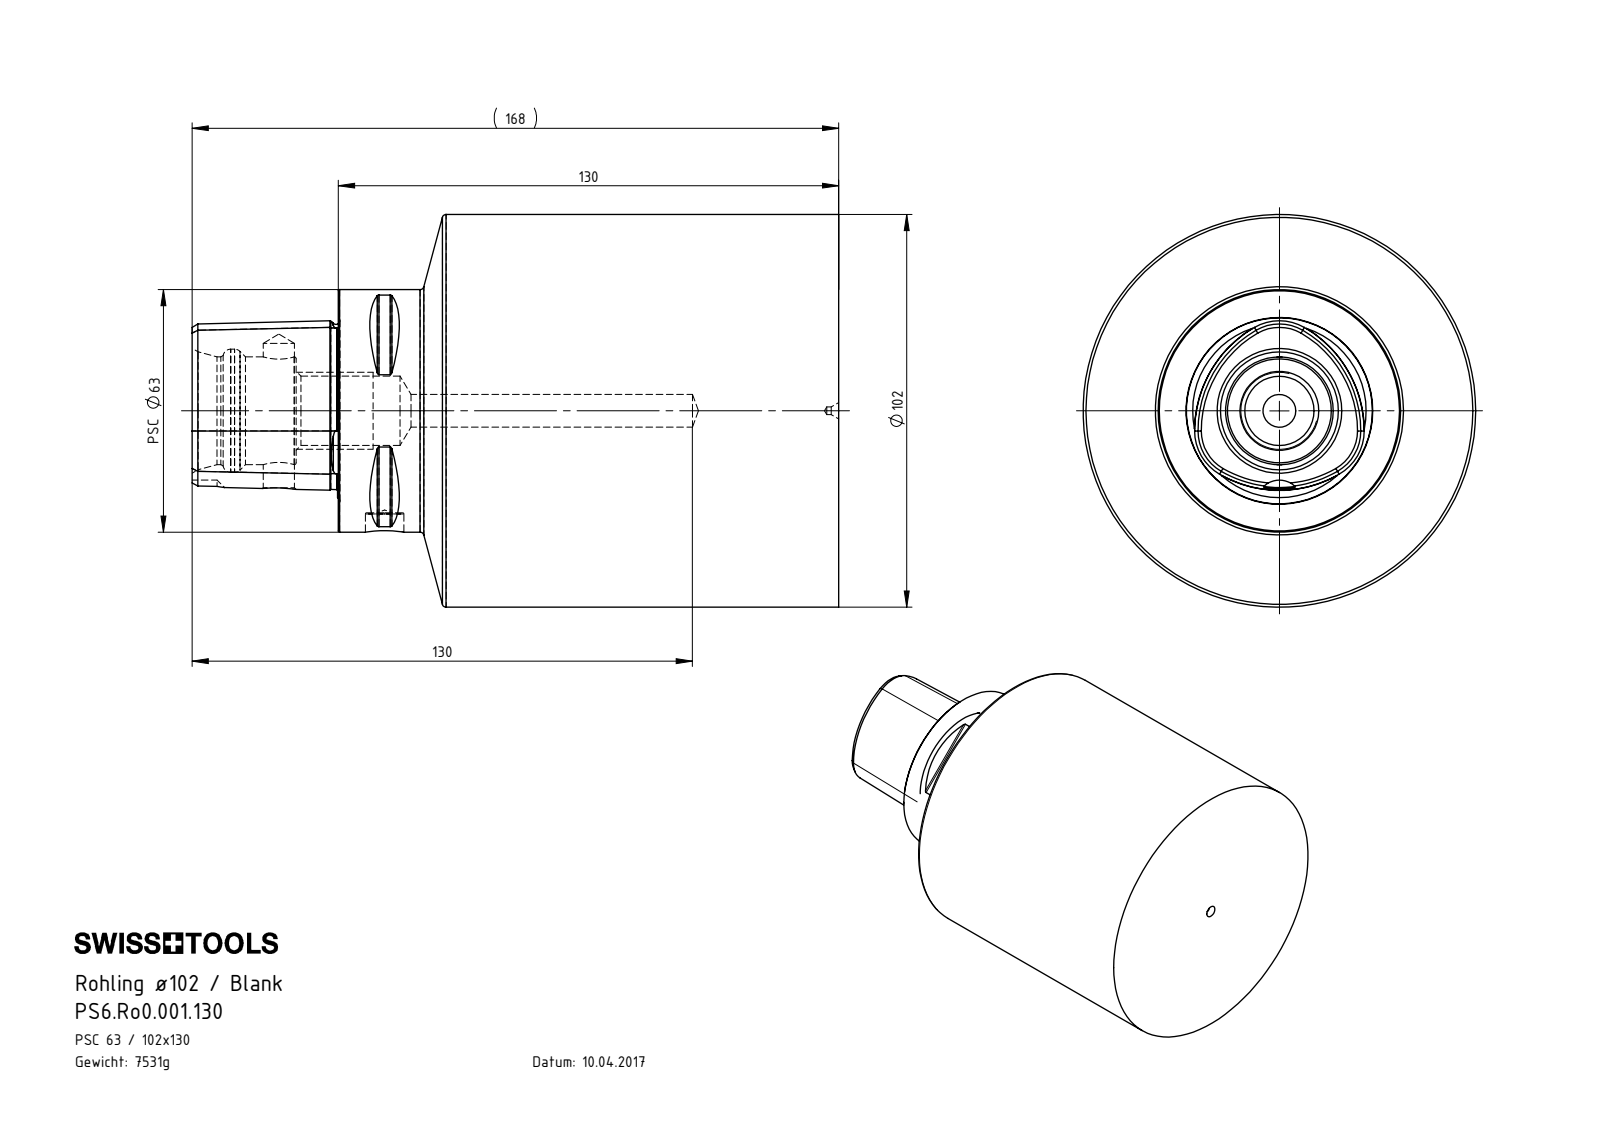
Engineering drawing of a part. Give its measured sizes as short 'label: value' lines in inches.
name: PS6-Ro0.001.130
written by: SolidWorks 2012 (CONFIG_CONTROL_DESIGN)
unit: in
bodies: 1 solid, 129 faces (19 planar, 29 cylindrical, 81 other)
size: 6.614 × 4.016 × 4.016
volume: 58.82 in³; area: 97.87 in²
holes: 1× ⌀0.079, 1× ⌀0.157, 1× ⌀0.319, 1× ⌀0.709, 1× ⌀1.102, 1× ⌀1.26
bosses: 1× ⌀4.016, 1× ⌀2.48
rounds: 8× R0.02, 1× R0.236
face distances: 5.118, 1.496, 6.614, 0.98, 1.063, 0.433, 5.551, 2.197, 1.488, 0.425
hole spacings: 1.083
